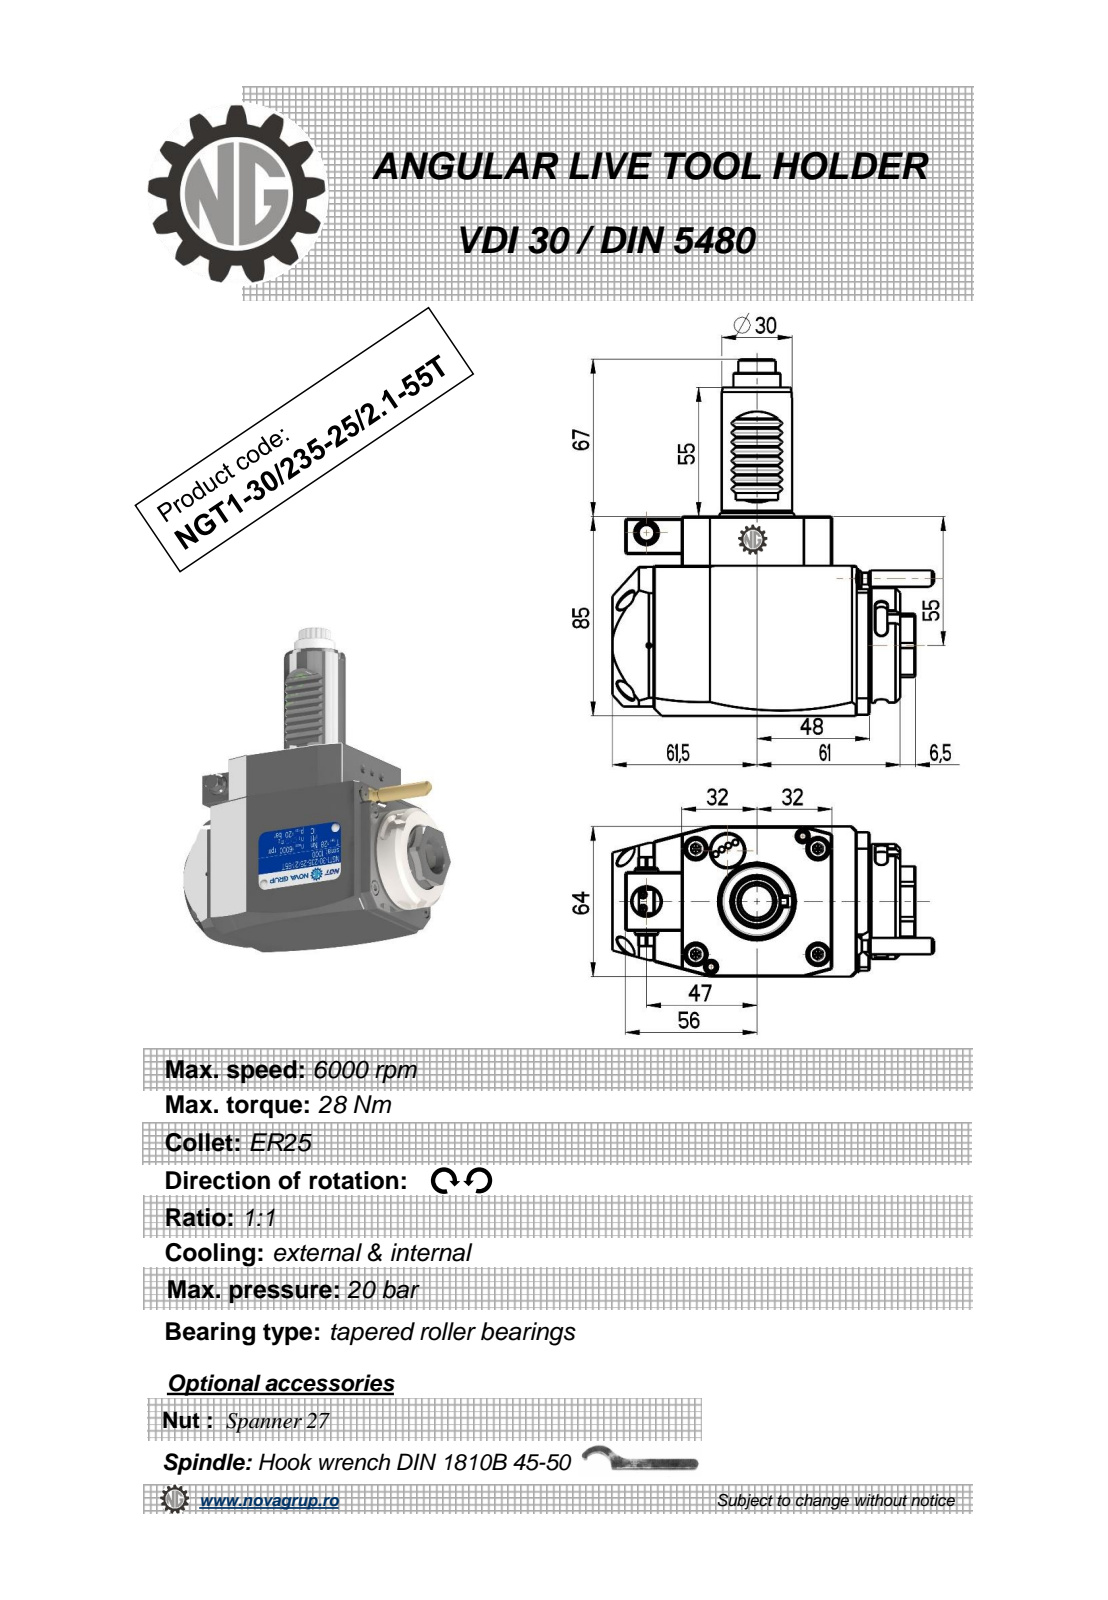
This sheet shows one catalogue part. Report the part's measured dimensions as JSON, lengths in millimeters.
{"part_name": "NGT1_30_235_25_1_1_55T", "step_written_by": "PRO/ENGINEER BY PARAMETRIC TECHNOLOGY CORPORATION, 2010280 (CONFIG_CONTROL_DESIGN)", "units": "millimeters", "bodies": {"solids": 1, "faces": 427, "planar": 186, "cylindrical": 153, "other": 88}, "overall_size": [152, 136.88, 64], "volume_mm3": 559077, "surface_area_mm2": 51039, "round_holes": [[2.5, 1], [3, 1], [9.5, 1], [12, 1], [18, 1]], "round_bosses_or_shafts": [[8, 2], [49, 1], [42, 1], [30, 1], [20, 1], [10, 1], [7, 1], [5, 1]], "partial_cylinders_radius": [[1.98, 36], [0.3, 8], [2.5, 6], [180, 2], [3.85, 1], [4.25, 1], [4.5, 1], [7.08, 1]], "face_to_face_distances": [64, 85, 16, 13, 109.5, 21, 80, 122.5, 29, 93.5], "hole_center_spacings": [26.17, 34.25, 46.5]}
